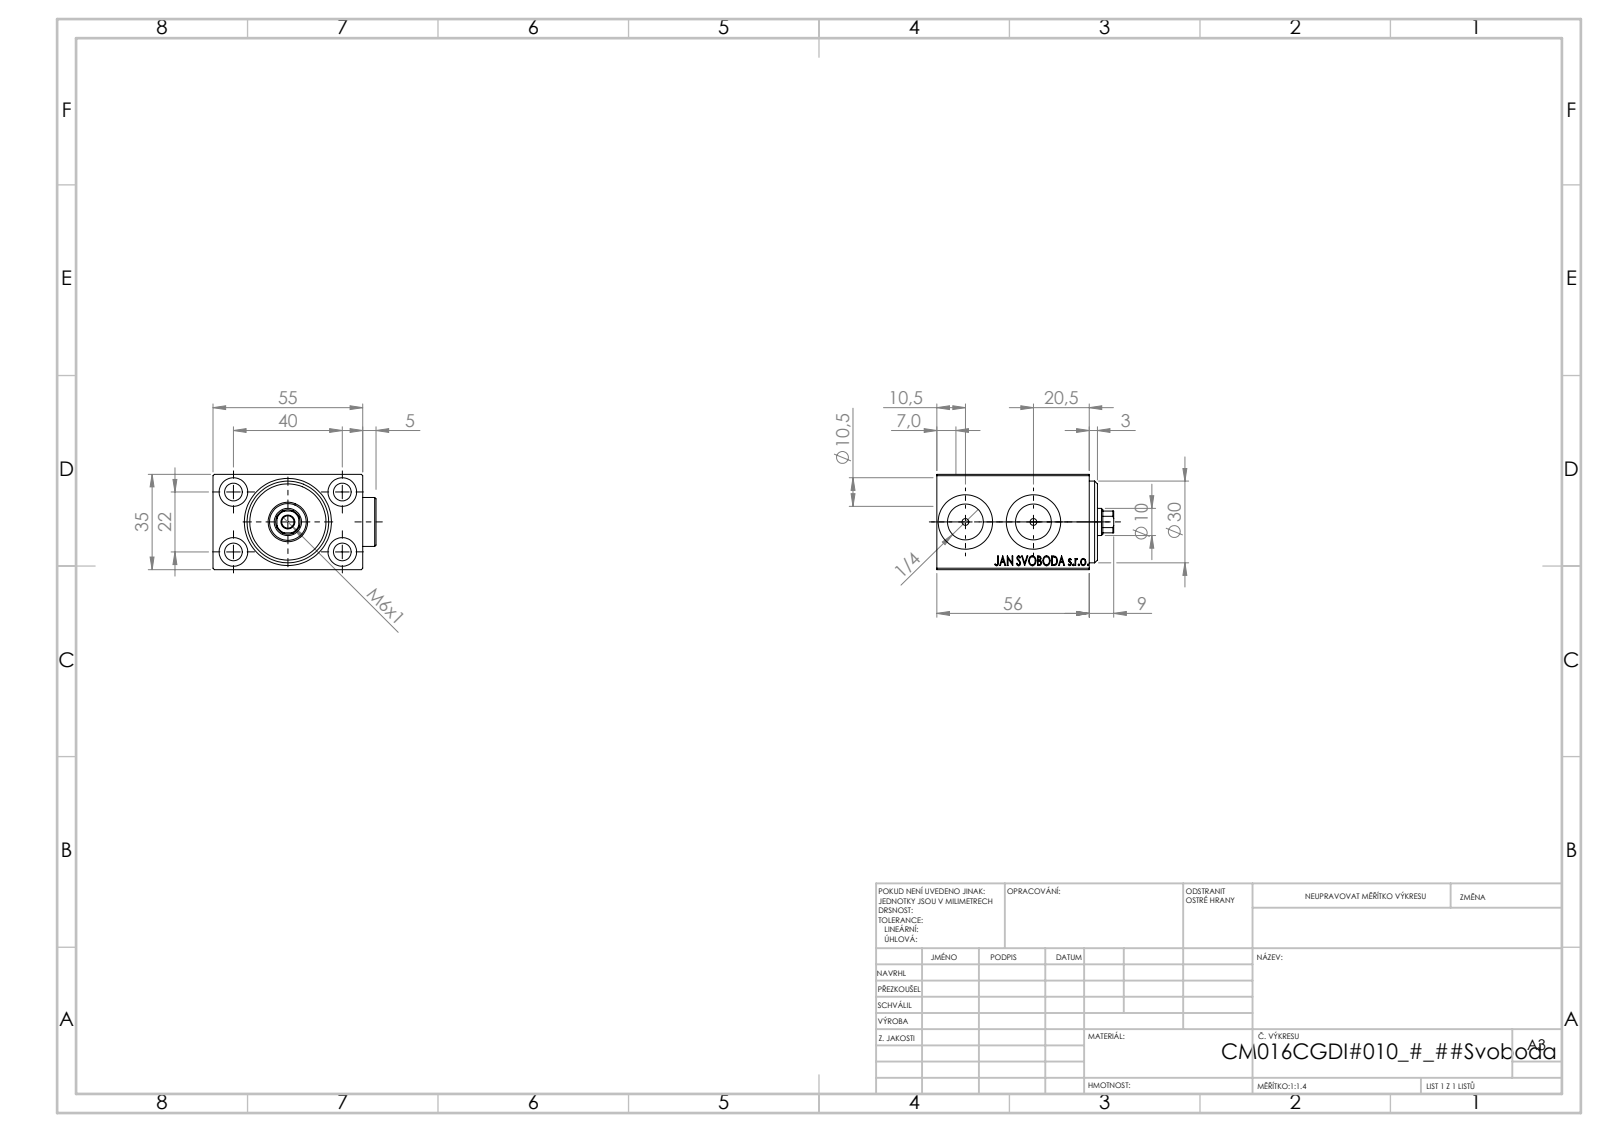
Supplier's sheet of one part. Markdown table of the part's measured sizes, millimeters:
| quantity | value |
| --- | --- |
| part name | V450CM_C_VCP; V450CM_C_Body; Zatka_OIL_PORT; V450CM_VC_B |
| STEP written by | SolidWorks 2019 (CONFIG_CONTROL_DESIGN) |
| units | millimeters |
| bodies | 5 solids, 919 faces (443 planar, 78 cylindrical, 398 other) |
| overall size | 65 × 59.9 × 35 |
| volume | 93 219 mm³ |
| surface area | 31 381 mm² |
| round holes (diameter × count) | 6.5 × 4, 10.5 × 4, 2.5 × 2, 13.16 × 2, 20 × 2, 4.5 × 1, 10 × 1, 13.5 × 1, 14.5 × 1, 16 × 1, 18 × 1, 30 × 1 |
| round bosses / shafts (diameter × count) | 18 × 2 |
| partial cylindrical surfaces (radius × count) | 4.5 × 1 |
| main face-to-face distances | 35, 5, 51, 55, 54.9, 56, 2, 42, 3, 8 |
| hole center spacings | 22.83, 22, 40, 45.65, 25 |
